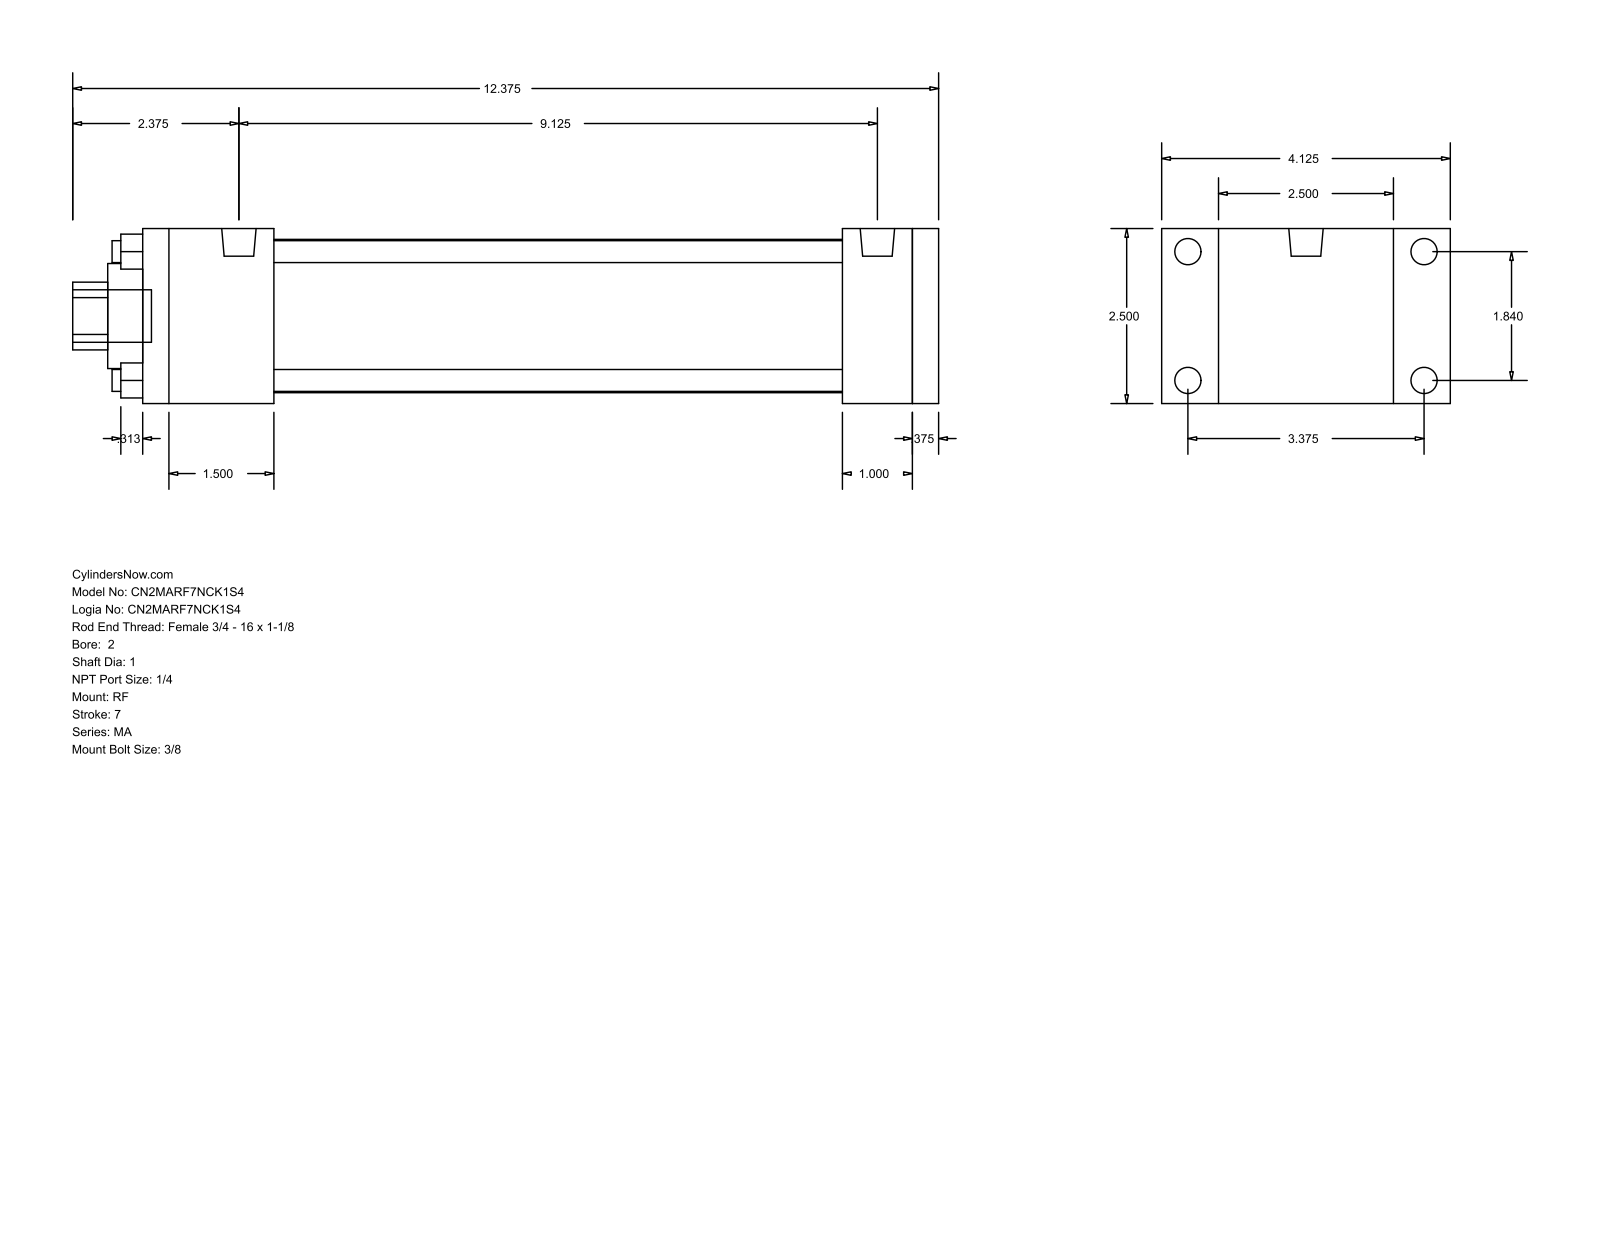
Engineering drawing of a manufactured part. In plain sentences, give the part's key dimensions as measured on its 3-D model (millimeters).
The part is named "MA_RF__0200_1". Its 3-D file was written by "GSSL Pune (CONFIG_CONTROL_DESIGN)". It is 0 solids with 92 faces: 64 planar, 28 cylindrical and 0 other. Overall it measures 314.32 by 104.78 by 63.5 millimeters. Round holes: 4 of diameter 7.94, 1 of diameter 25.4, 1 of diameter 38.1, 1 of diameter 55.63. Round bosses or shafts: 4 of diameter 9.53, 4 of diameter 7.94, 2 of diameter 12.49, 1 of diameter 19.05. Partial cylindrical surfaces (rounded edges, fillets, slot ends): 1 of radius 12.29. The main face-to-face distances are 63.5, 279.4, 9.52, 288.92, 25.4, 20.64, 12.7, 47.63, 231.77, 241.29. The hole center spacings are 33.05, 46.74, 66.1.
